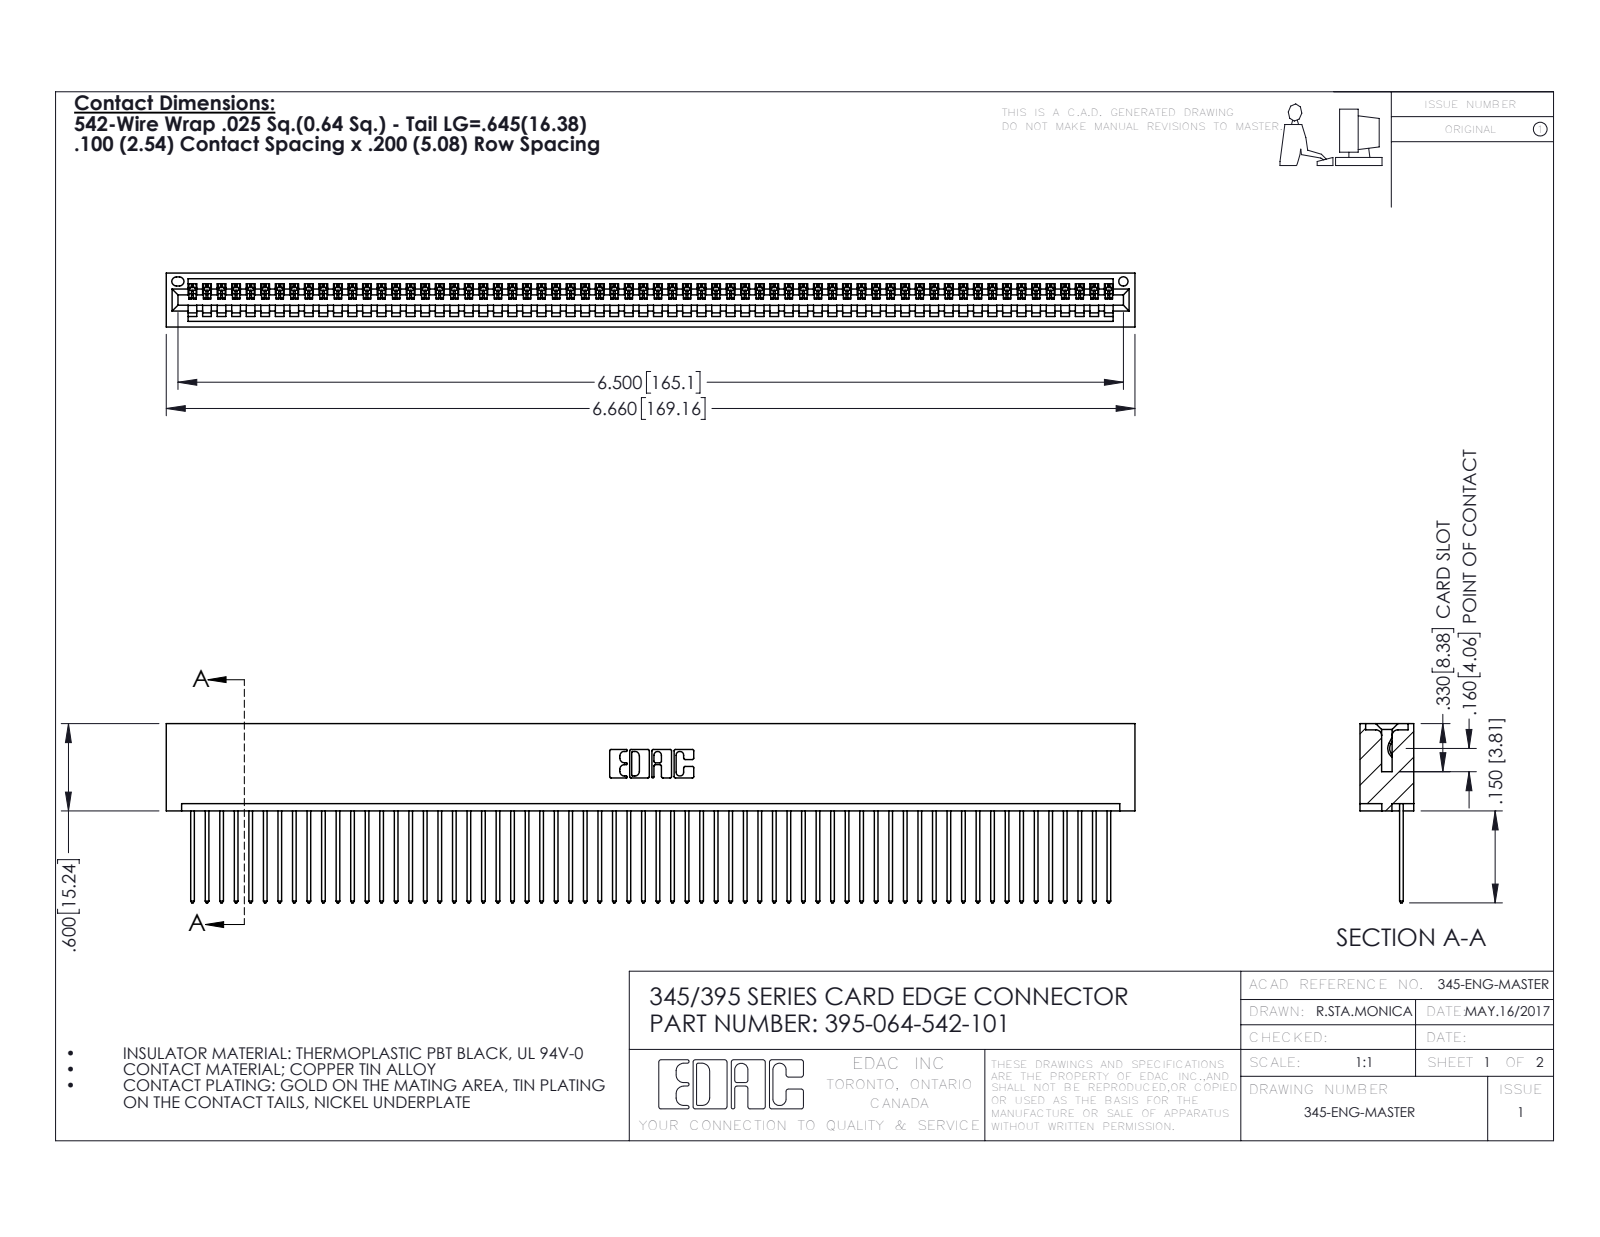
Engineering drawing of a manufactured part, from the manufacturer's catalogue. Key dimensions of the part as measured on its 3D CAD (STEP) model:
Part name (STEP PRODUCT): 345-292-001_345-293-142; 395-064-542-101; 345 Part_No Mounting Lugs
STEP written by: SolidWorks 2016 (CONFIG_CONTROL_DESIGN)
Units: inches
Bodies: 65 solids, 3830 faces (2636 planar, 1194 cylindrical, 0 other)
Overall size (bounding box): 6.66 × 1.232 × 0.37
Volume: 1.036 in³ · Surface area: 37.12 in²
Round holes (diameter × count): ⌀0.064 ×1
Partial cylindrical surfaces — rounded edges, fillets, slot ends (radius × count): R0.006 ×128, R0.01 ×128, R0.01 ×22, R0.007 ×6, R0.031 ×6, R0.026 ×3, R0.031 ×2, R0.04 ×2
Main face-to-face distances: 0.072, 0.298, 0.098, 0.272, 0.025, 0.37, 0.2, 0.225, 0.149, 0.072
